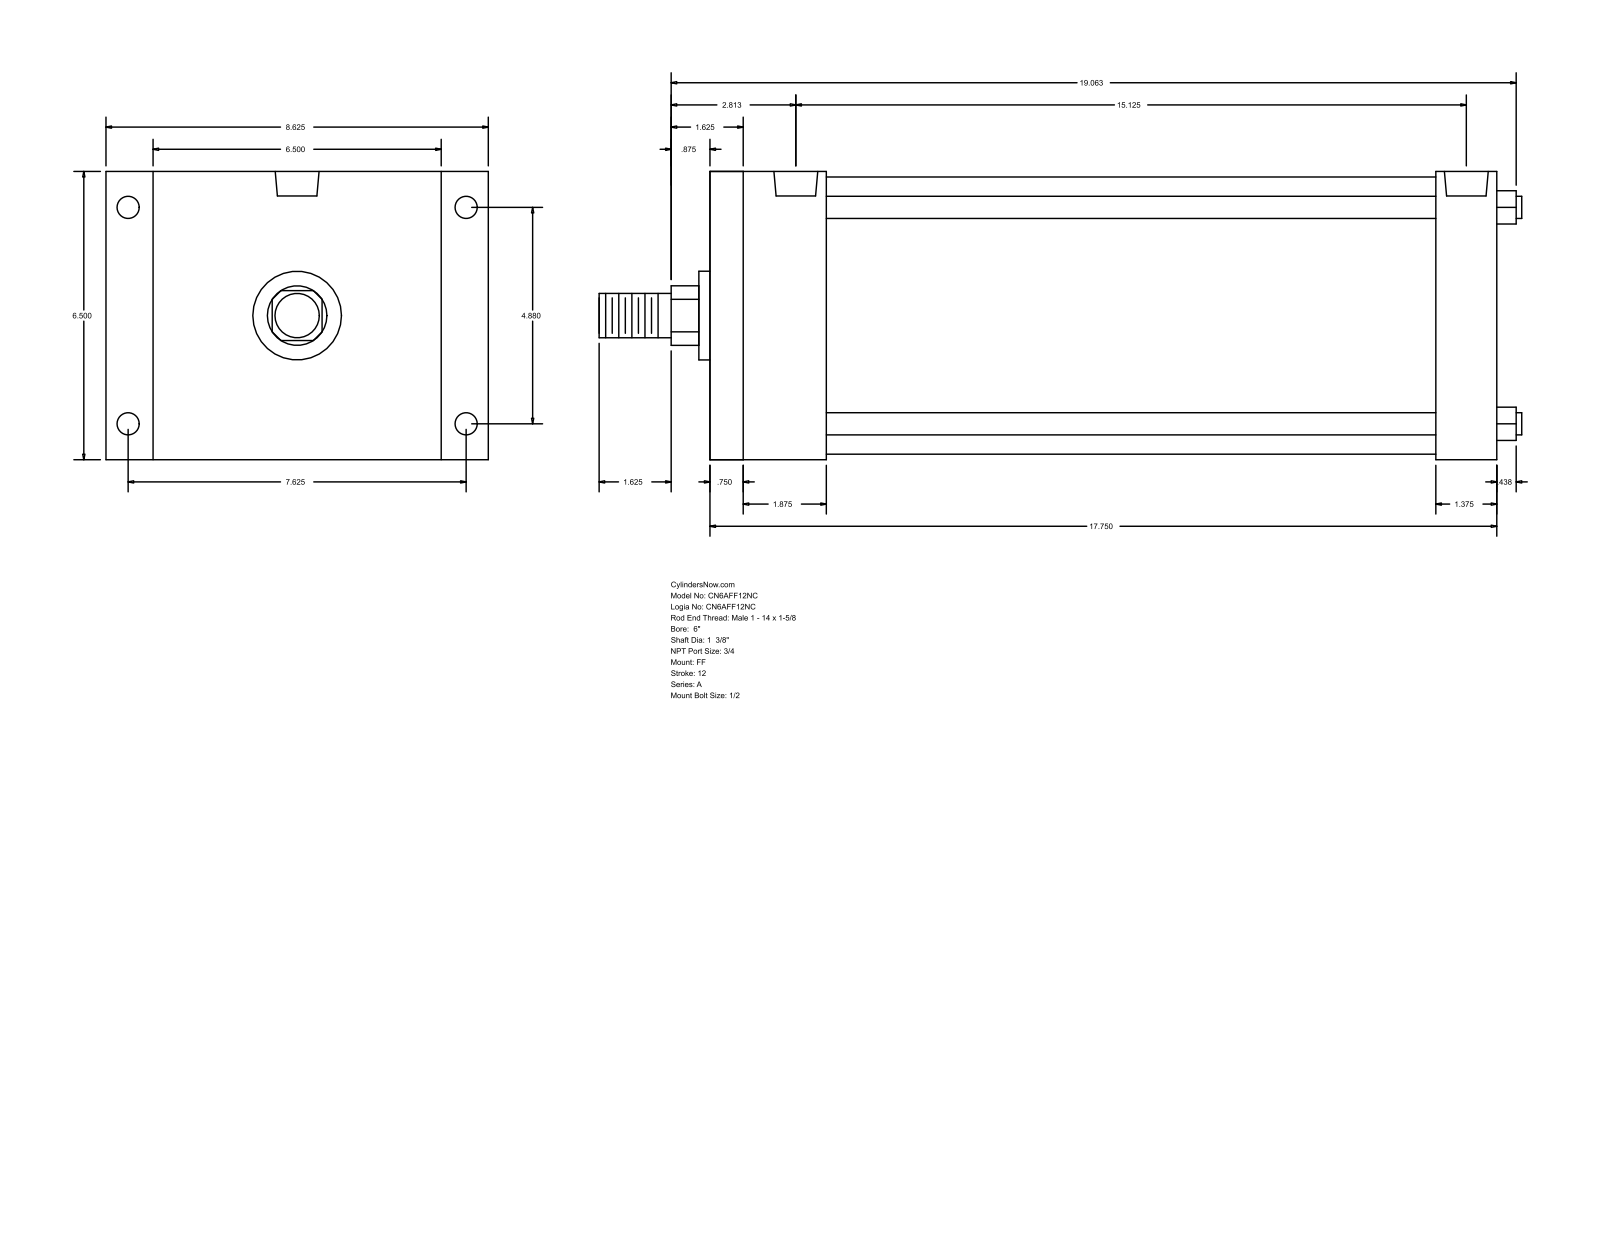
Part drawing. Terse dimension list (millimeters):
name: A_FF__0600_1.375
written by: GSSL Pune (CONFIG_CONTROL_DESIGN)
unit: mm
bodies: 0 solids, 92 faces (64 planar, 28 cylindrical, 0 other)
size: 528.64 × 219.07 × 165.1
holes: 4× ⌀12.7, 4× ⌀15.08, 2× ⌀25.12
bosses: 4× ⌀12.7, 1× ⌀158.75, 1× ⌀50.8, 1× ⌀34.92, 1× ⌀25.4
rounds: 1× R17.06
face distances: 165.1, 450.84, 19.04, 431.8, 66.67, 47.63, 384.17, 415.92, 396.88, 349.25
hole spacings: 5.56, 123.96, 193.68, 229.95, 373.05, 378.61, 384.17
